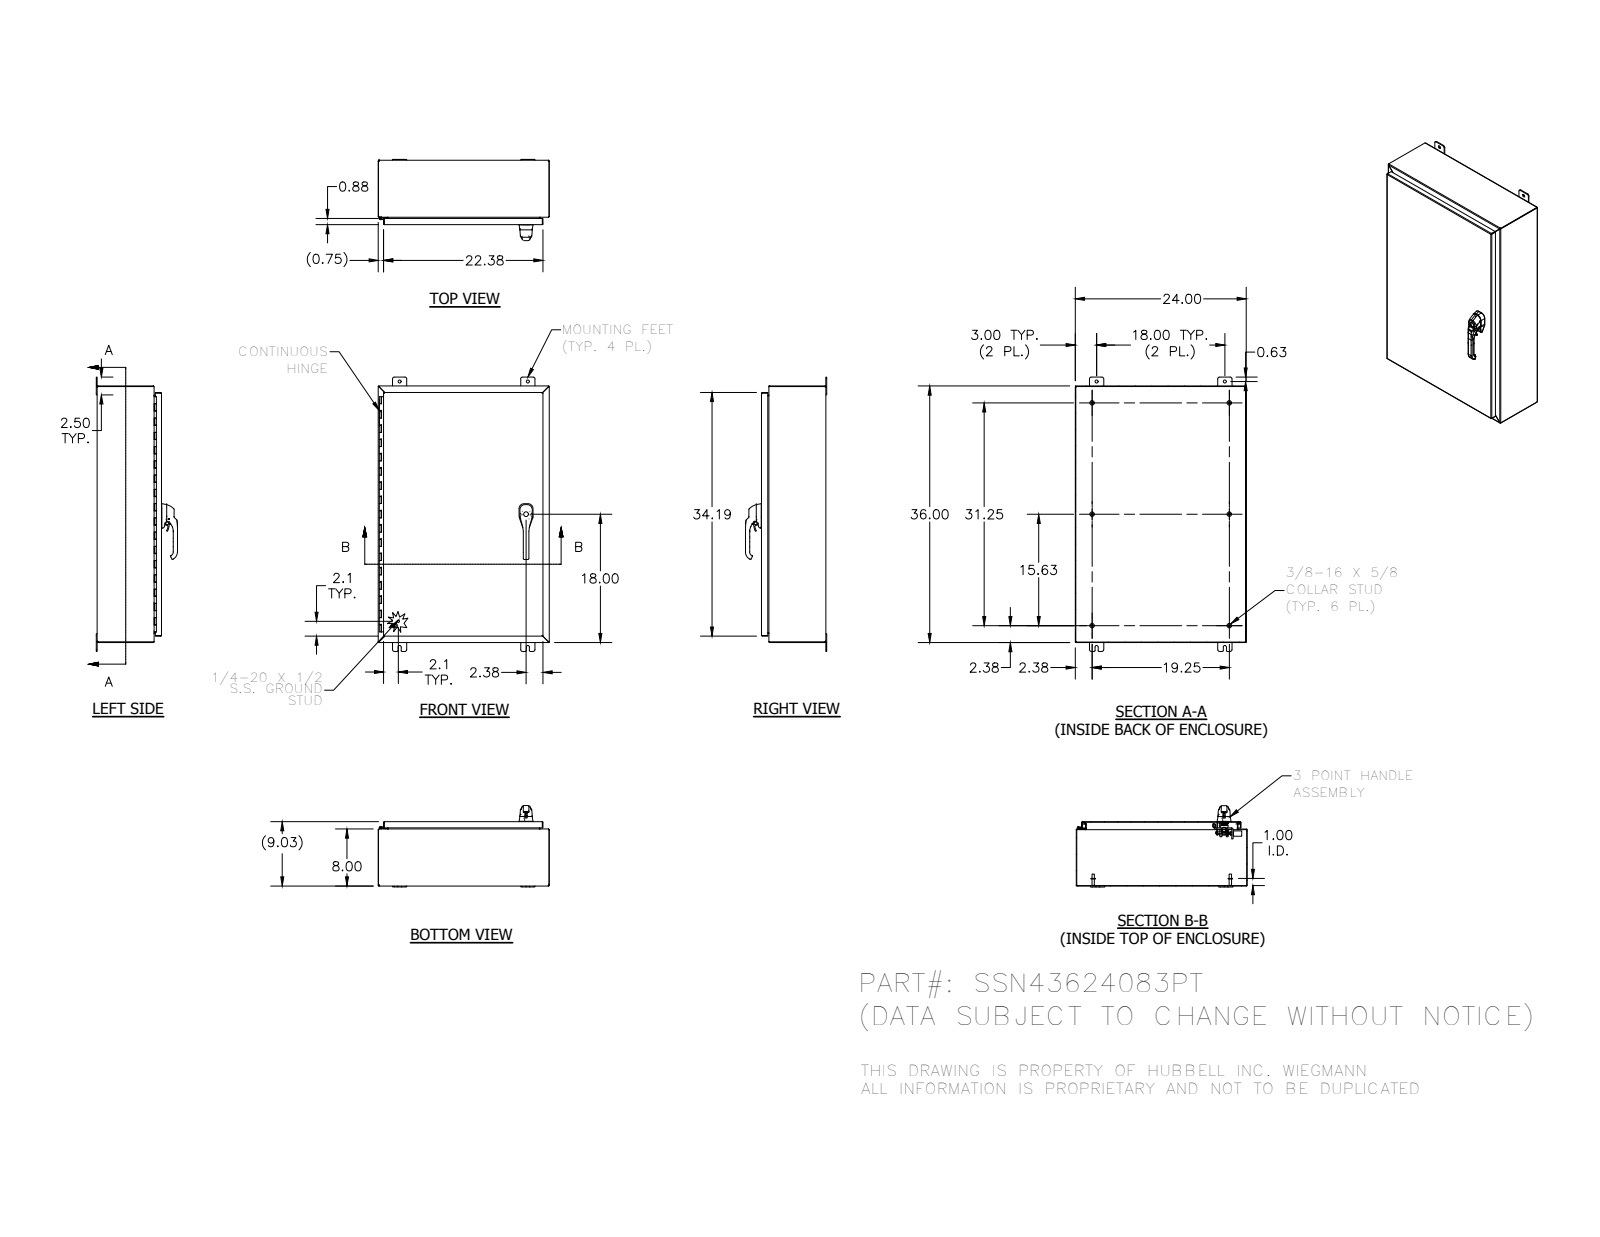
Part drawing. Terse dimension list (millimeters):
name: 1225-05; SSN43624083PTBKP; 328140T; PLASTIC-ROLLER-CAM_AF0_ASM (+8 more)
written by: SolidWorks 2014 (AUTOMOTIVE_DESIGN)
unit: mm
bodies: 58 solids, 3221 faces (1088 planar, 1344 cylindrical, 789 other)
size: 977.9 × 609.6 × 289.8
volume: 4 107 000 mm³; area: 4 198 000 mm²
holes: 8× ⌀6.7, 4× ⌀4.7, 4× ⌀11.1, 3× ⌀5.4, 3× ⌀7.1, 2× ⌀6.1, 2× ⌀6.4, 2× ⌀6.4, 2× ⌀8, 2× ⌀10.2, 2× ⌀10.2, 2× ⌀10.5
bosses: 6× ⌀15.9, 6× ⌀8.4, 3× ⌀6, 2× ⌀25.4, 2× ⌀14.3, 2× ⌀13.5, 2× ⌀13.5, 2× ⌀12.7
rounds: 172× R0.5, 113× R0.3, 26× R3.2, 24× R0.8, 21× R0.5, 20× R2.7, 20× R6.4, 16× R0.6
face distances: 1.9, 227.6, 225.7, 229.4, 607.7, 912.5, 201.3, 26.2, 605.8, 609.6
hole spacings: 9.7, 12.5, 19.3, 22.5, 671.3, 5.9, 6.6, 9.7
